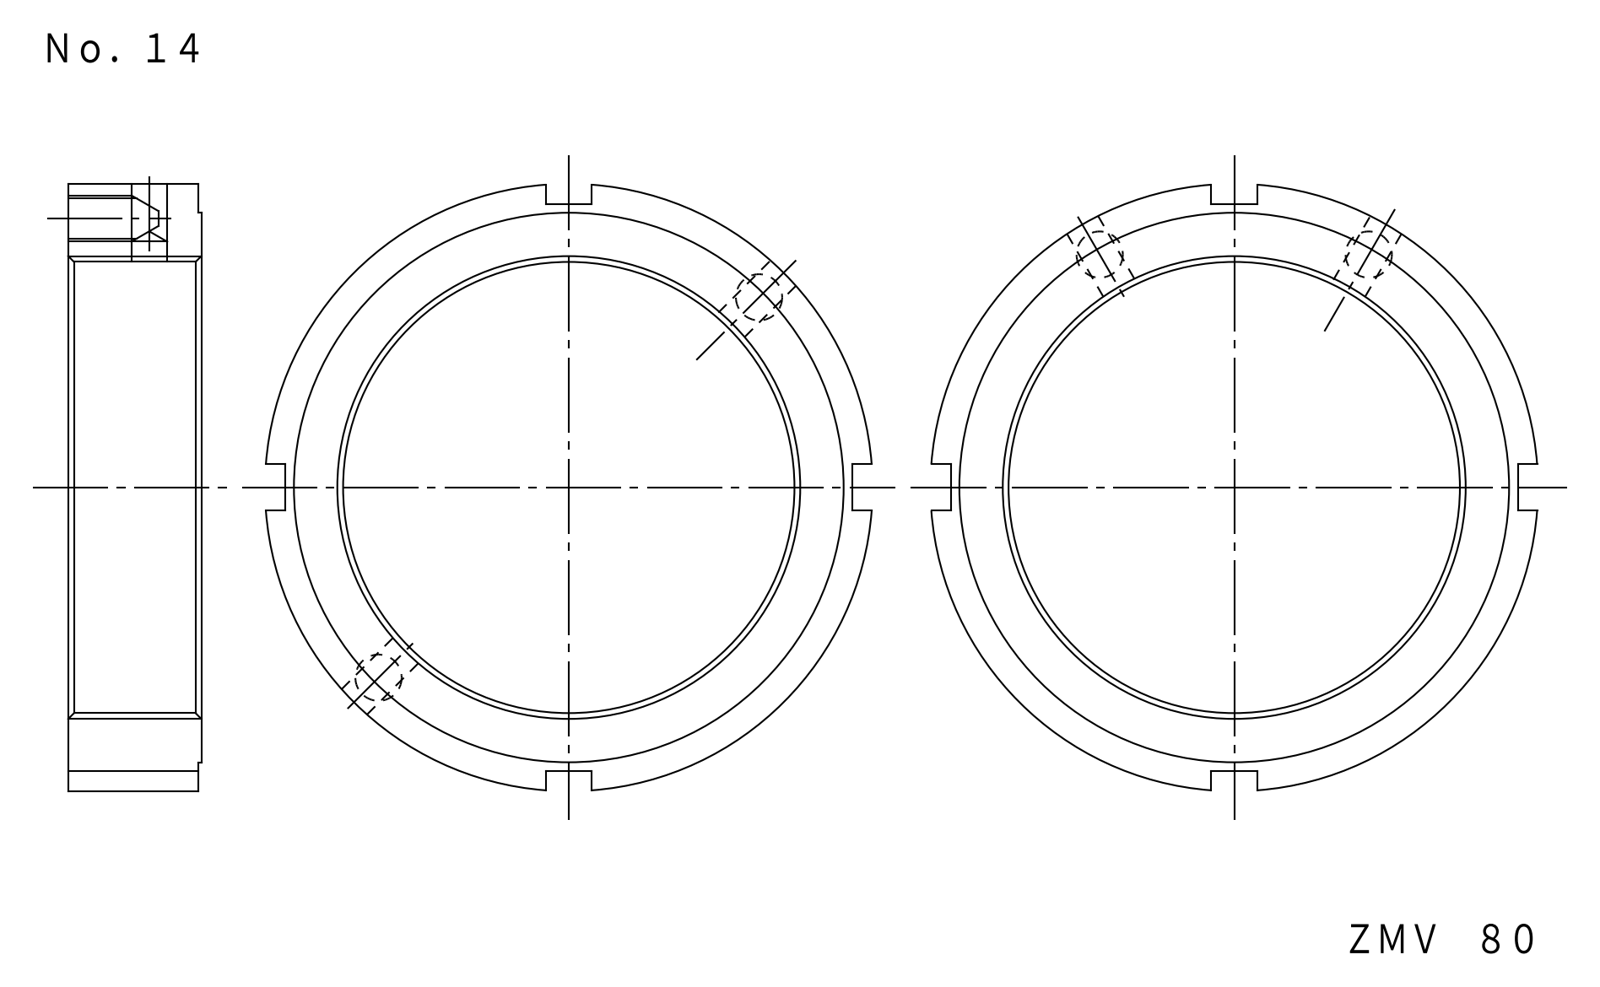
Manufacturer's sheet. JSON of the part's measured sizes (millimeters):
{"part_name": "FKD ZMV80", "step_written_by": "Autodesk Inventor LT (CONFIG_CONTROL_DESIGN)", "units": "millimeters", "bodies": {"solids": 1, "faces": 29, "planar": 15, "cylindrical": 10, "other": 4}, "overall_size": [104.69, 104.69, 23], "volume_mm3": 78727, "surface_area_mm2": 21716, "round_holes": [[6.2, 2], [6.65, 2], [80, 1]], "round_bosses_or_shafts": [[105, 1], [95, 1]], "face_to_face_distances": [23, 0.5, 22.5, 45, 53, 98, 8], "hole_center_spacings": [46.5, 93]}
